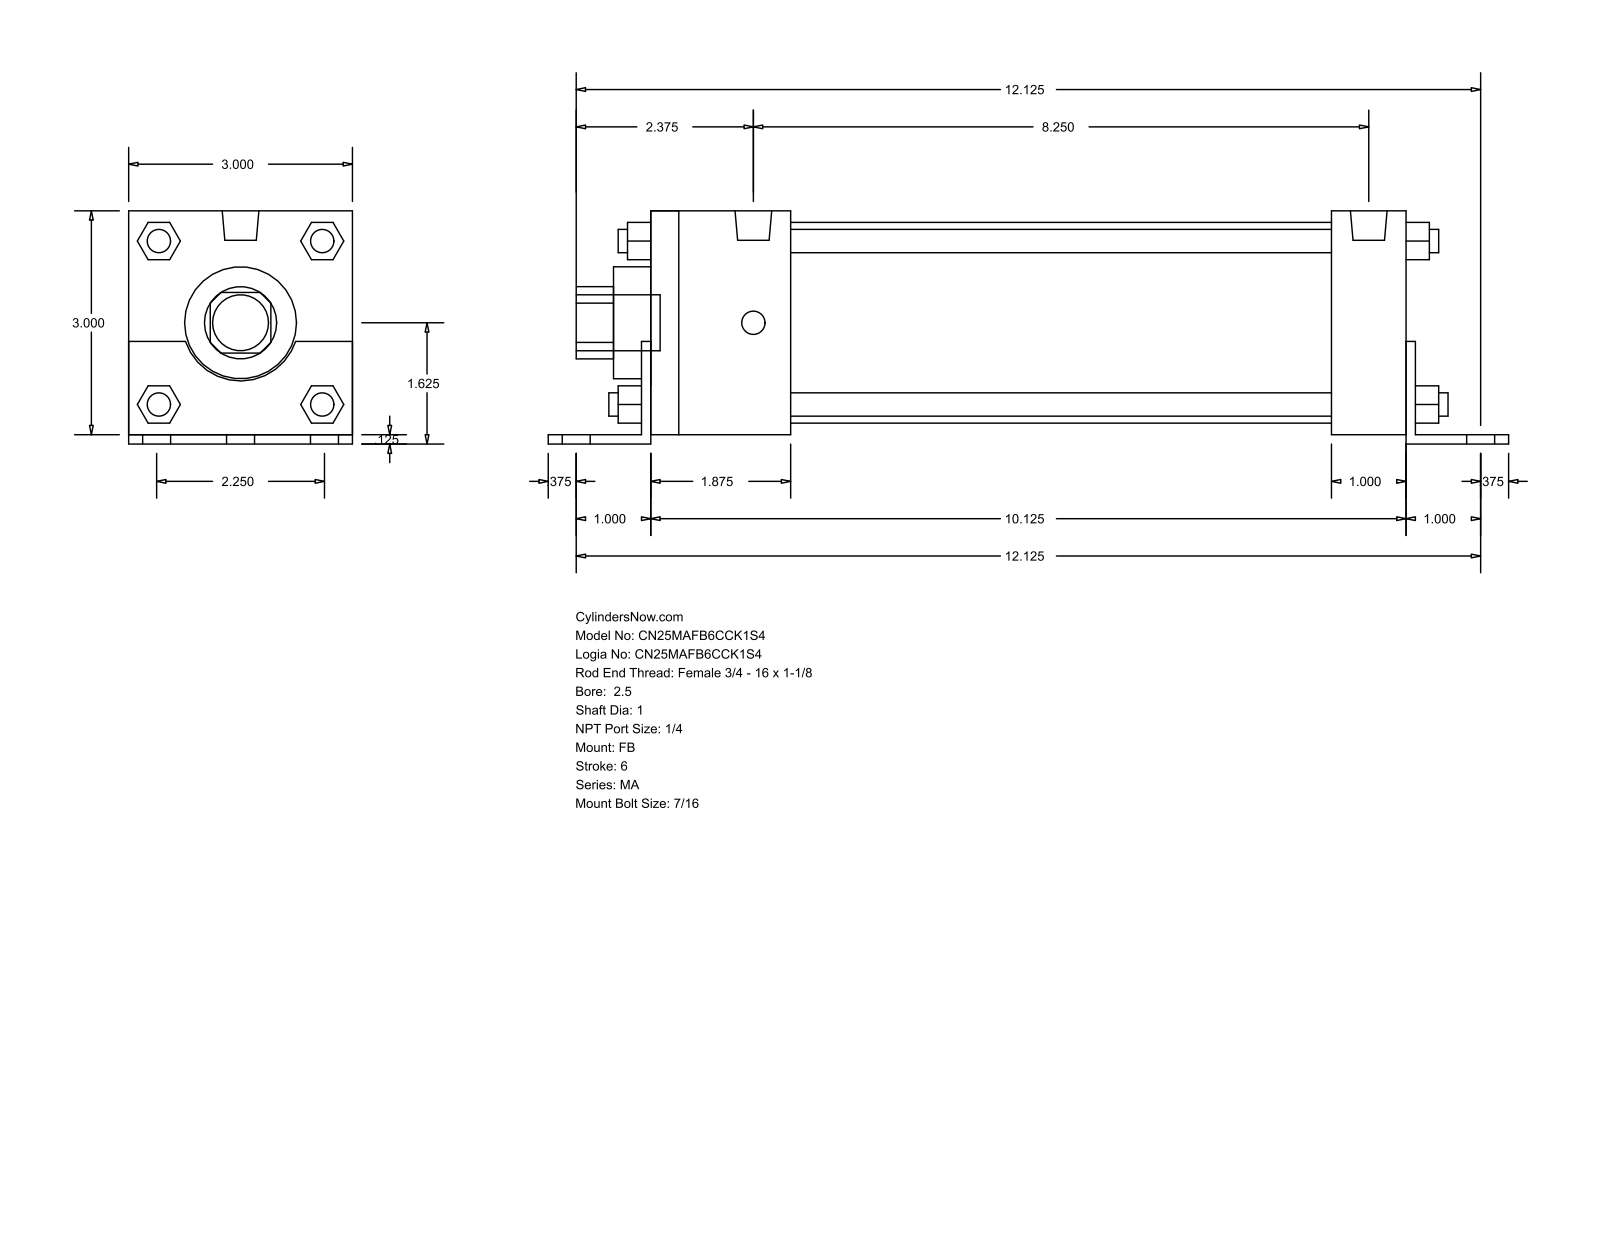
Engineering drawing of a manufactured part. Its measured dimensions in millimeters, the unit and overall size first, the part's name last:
Units: millimetres
Overall size (bounding box): 327.02 × 79.38 × 76.2
Round holes (diameter × count): ⌀25.4 ×1, ⌀38.1 ×1, ⌀68.33 ×1
Round bosses / shafts (diameter × count): ⌀7.94 ×8, ⌀11.11 ×6, ⌀12.49 ×2, ⌀19.05 ×1
Partial cylindrical surfaces — rounded edges, fillets, slot ends (radius × count): R12.29 ×1, R19.81 ×1
Main face-to-face distances: 76.2, 3.17, 79.37, 257.17, 3.18, 12.7, 260.35, 28.57, 47.63, 209.54
Bodies: 0 solids, 140 faces (105 planar, 35 cylindrical, 0 other)
Part name (STEP PRODUCT): MA_FB__0250_1
STEP written by: GSSL Pune (CONFIG_CONTROL_DESIGN)
